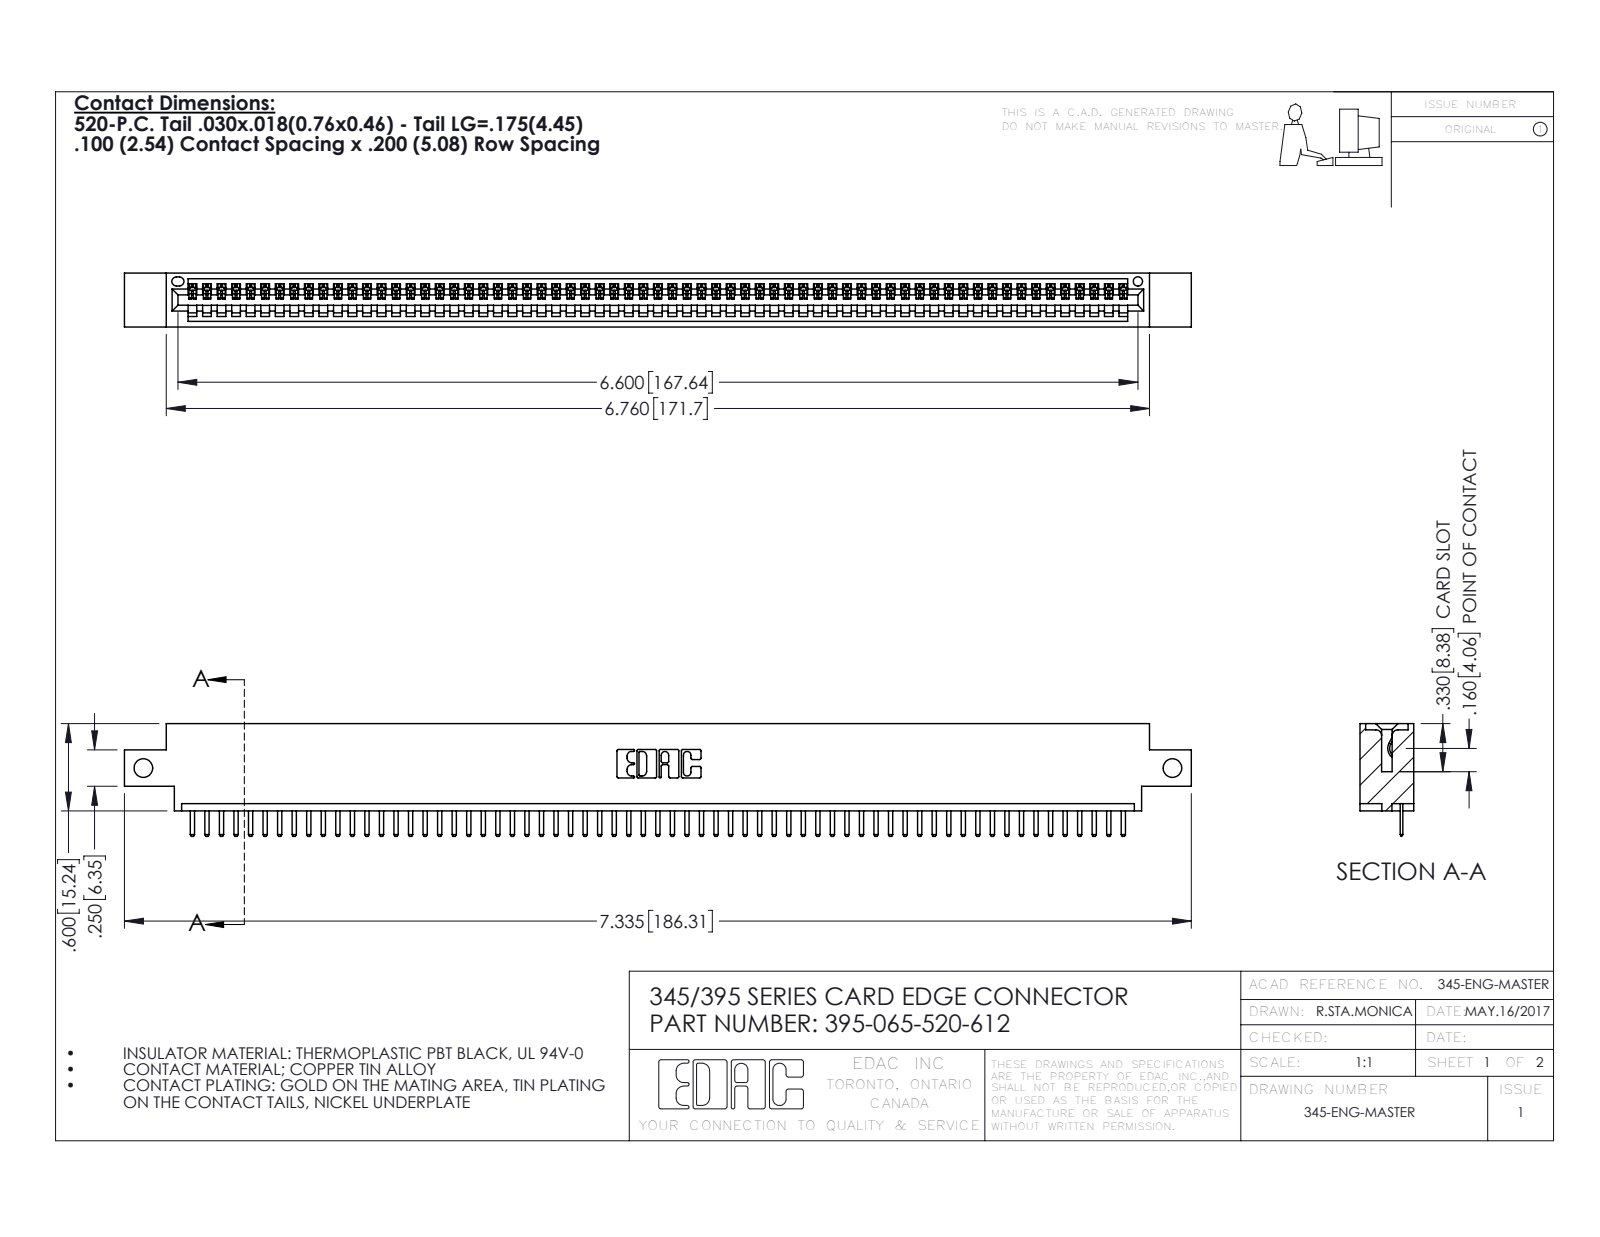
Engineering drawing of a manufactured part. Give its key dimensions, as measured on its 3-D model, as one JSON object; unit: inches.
{"part_name": "345 Part_0.170 Offset - Side Mount; 345-292-001_345-293-120; 395-065-520-612", "step_written_by": "SolidWorks 2016 (CONFIG_CONTROL_DESIGN)", "units": "inches", "bodies": {"solids": 66, "faces": 4160, "planar": 2814, "cylindrical": 1346, "other": 0}, "overall_size": [7.335, 0.775, 0.37], "volume_in3": 1.068, "surface_area_in2": 35.55, "round_holes": [[0.128, 2], [0.064, 1]], "partial_cylinders_radius": [[0.01, 132], [0.006, 130], [0.01, 22], [0.007, 6], [0.031, 6], [0.026, 3], [0.031, 2], [0.04, 2]], "face_to_face_distances": [0.298, 0.072, 0.37, 0.2, 0.098, 0.272, 0.025, 0.225, 0.072, 0.175], "hole_center_spacings": [7.075]}
